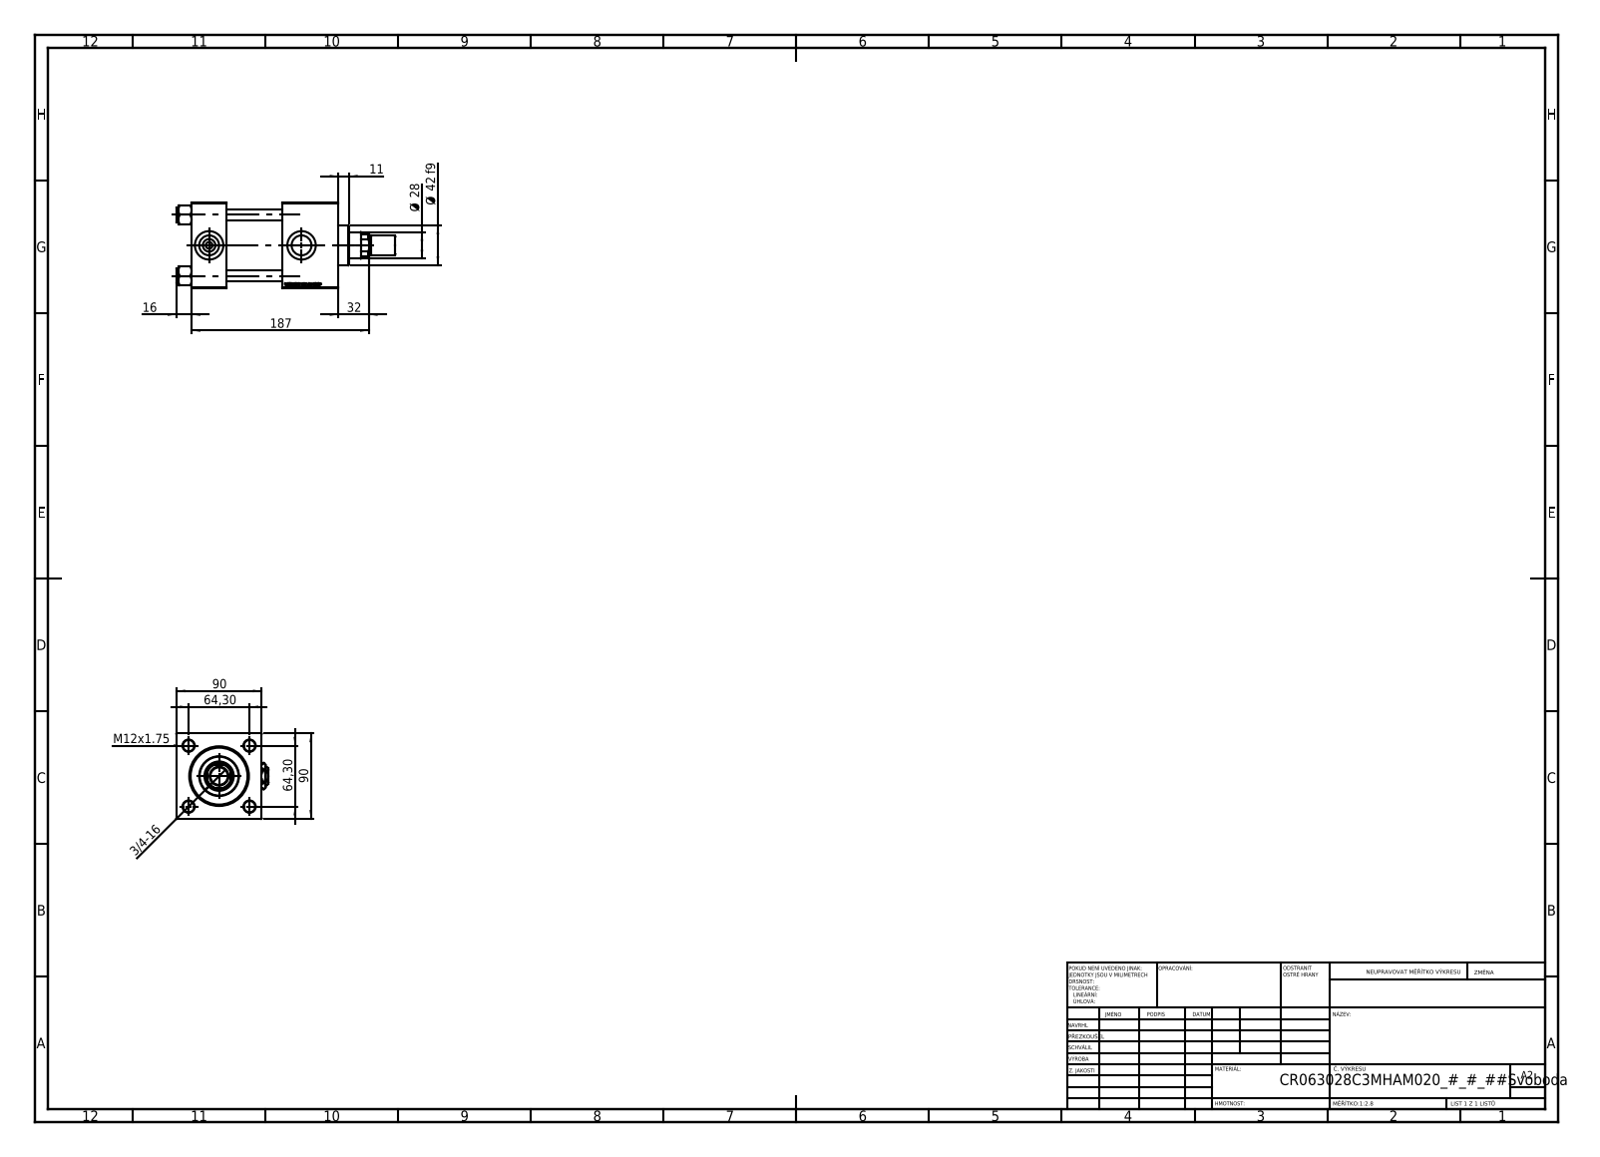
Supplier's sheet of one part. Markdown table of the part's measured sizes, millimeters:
| quantity | value |
| --- | --- |
| part name | V215CR_C_Body; V215CR_C_TYCINKA; NUT_M5_C; ROD_END_AH (+3 more) |
| STEP written by | SolidWorks 2019 (CONFIG_CONTROL_DESIGN) |
| units | millimeters |
| bodies | 14 solids, 1264 faces (578 planar, 102 cylindrical, 584 other) |
| overall size | 231 × 97 × 90 |
| volume | 949 136 mm³ |
| surface area | 186 349 mm² |
| round holes (diameter × count) | 12 × 4, 7 × 2, 20.96 × 2, 30 × 2, 18.5 × 1, 28 × 1, 31 × 1, 50 × 1, 60 × 1, 63 × 1 |
| round bosses / shafts (diameter × count) | 15 × 4, 69 × 1, 42 × 1, 20 × 1, 18 × 1 |
| partial cylindrical surfaces (radius × count) | 13.5 × 1 |
| main face-to-face distances | 90, 59, 37, 118, 155, 96, 126.3, 89.3, 30.3, 28.7 |
| hole center spacings | 45.47, 64.3, 90.93, 97.5 |
